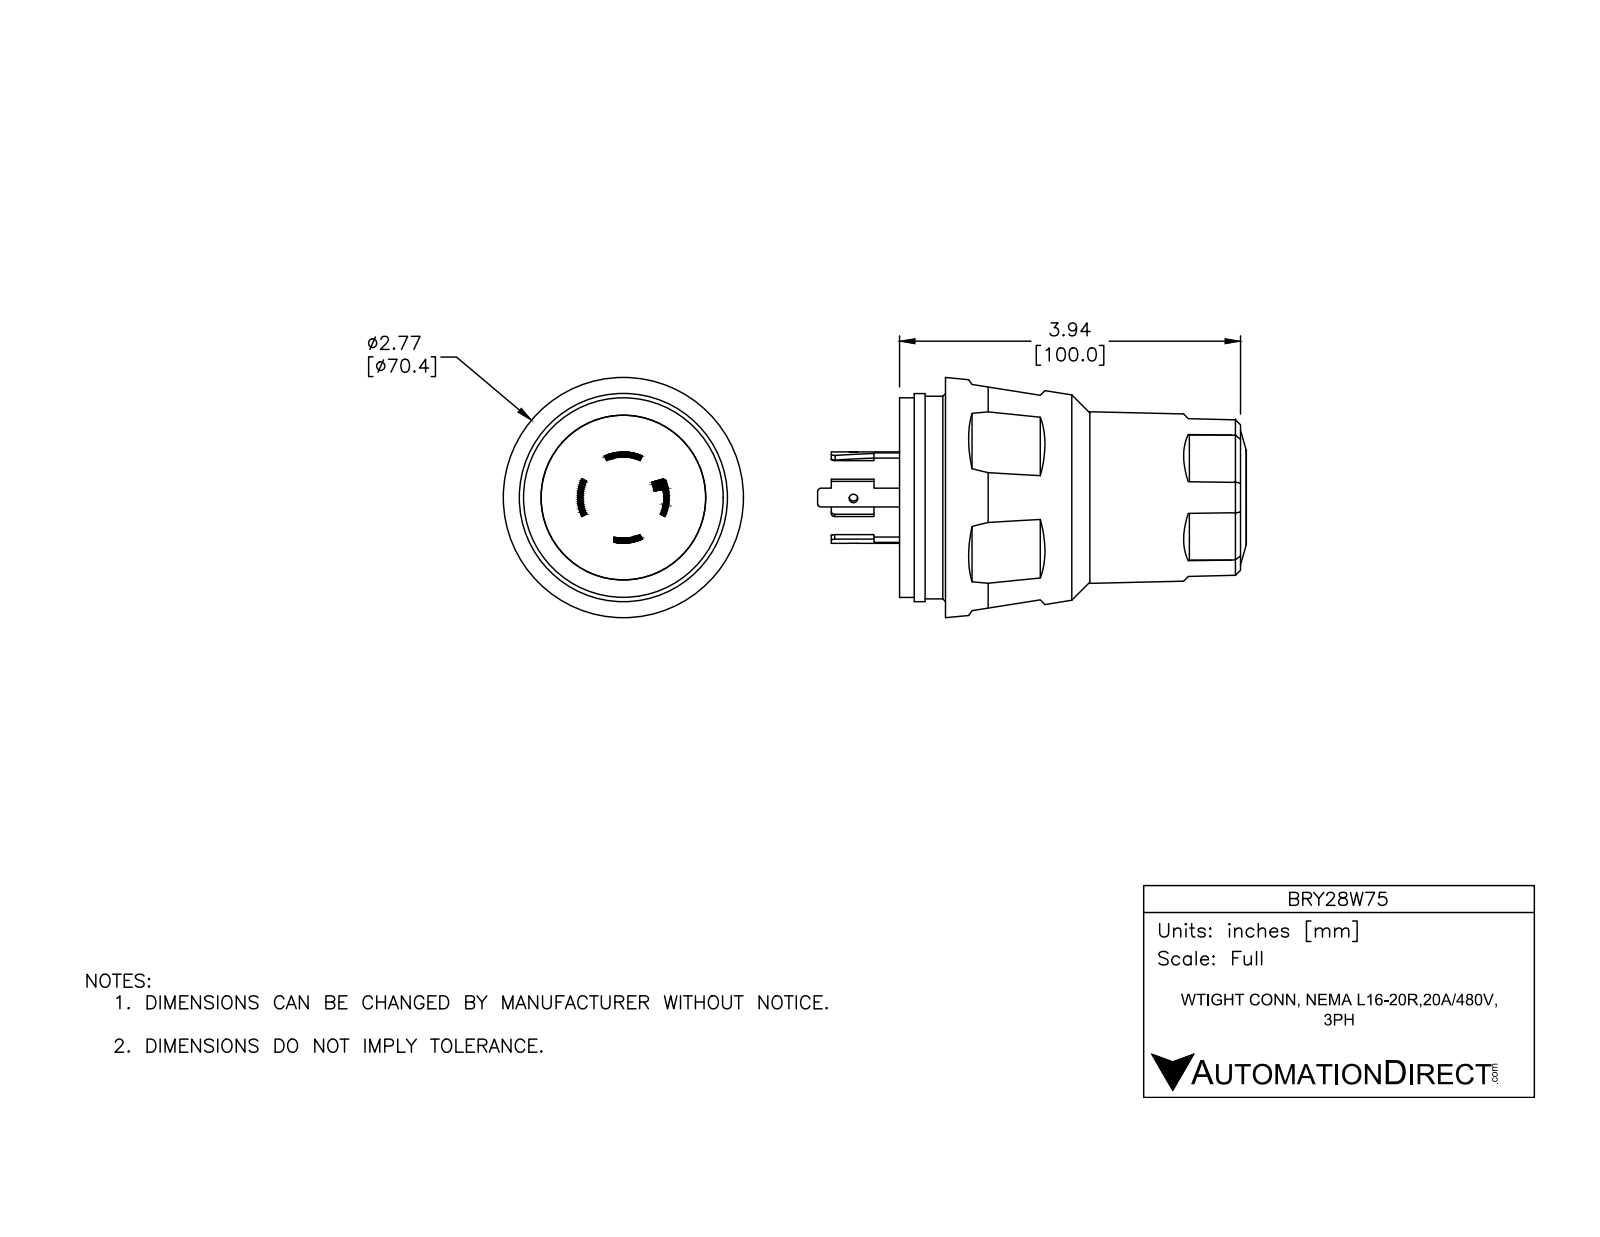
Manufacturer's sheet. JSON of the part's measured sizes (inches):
{"part_name": "BRY28W76", "step_written_by": "SolidWorks 2016 (AUTOMOTIVE_DESIGN)", "units": "inches", "bodies": {"solids": 8, "faces": 202, "planar": 116, "cylindrical": 63, "other": 23}, "overall_size": [4.948, 2.772, 2.772], "volume_in3": 14.59, "surface_area_in2": 69.57, "round_holes": [[0.098, 4], [1, 1], [1.902, 1]], "round_bosses_or_shafts": [[2.402, 1], [2.339, 1], [2.303, 1], [1.898, 1], [1.551, 1]], "partial_cylinders_radius": [[0.039, 11], [0.449, 1], [0.469, 1], [0.528, 1], [0.547, 1]], "face_to_face_distances": [0.276, 3.031, 3.307, 2.776, 0.256, 0.531, 0.551, 3.327, 3.583, 3.858], "hole_center_spacings": [0.02]}
